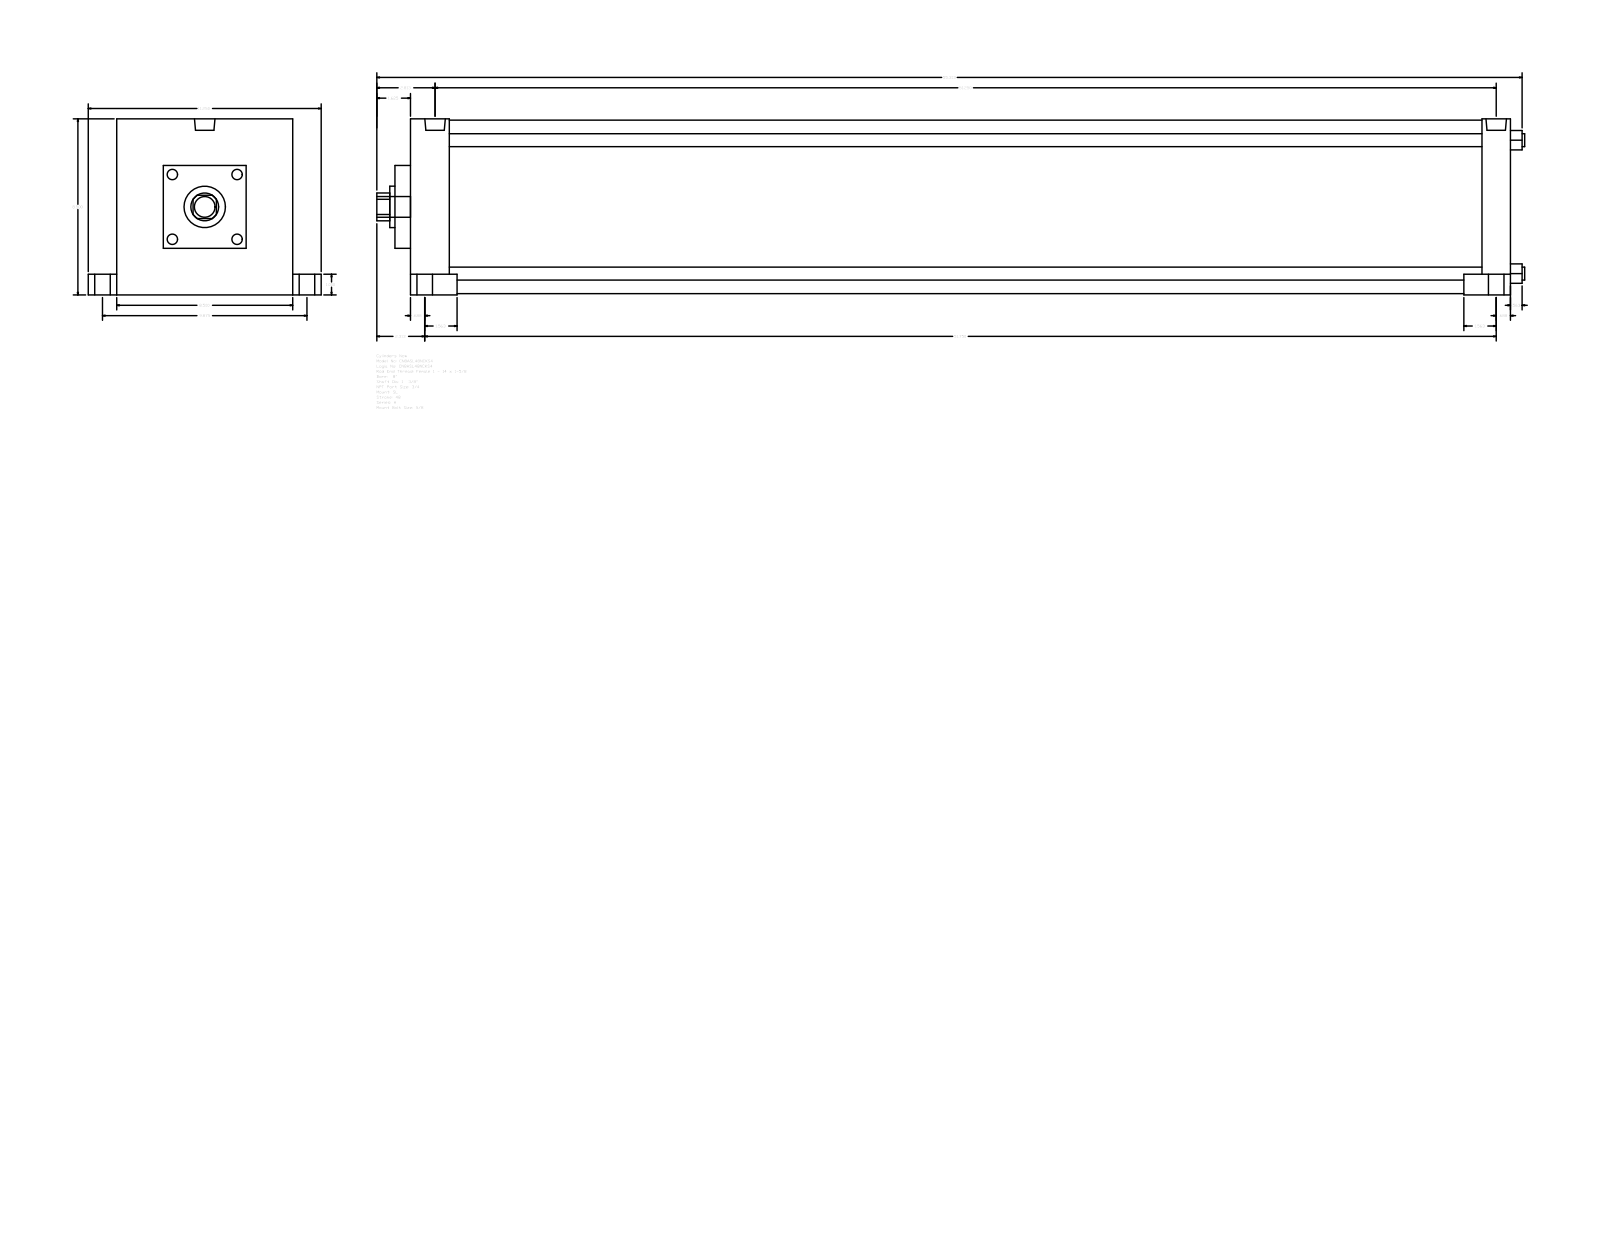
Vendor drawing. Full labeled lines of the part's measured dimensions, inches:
Part name (STEP PRODUCT): A_SL__0800_1.375
STEP written by: GSSL Pune (CONFIG_CONTROL_DESIGN)
Units: inches
Bodies: 0 solids, 117 faces (85 planar, 32 cylindrical, 0 other)
Overall size (bounding box): 55.437 × 11.25 × 8.5
Round holes (diameter × count): ⌀0.625 ×4, ⌀1.375 ×1, ⌀2 ×1, ⌀8.375 ×1
Round bosses / shafts (diameter × count): ⌀1 ×5, ⌀0.75 ×4, ⌀0.594 ×4, ⌀0.989 ×2
Partial cylindrical surfaces — rounded edges, fillets, slot ends (radius × count): R0.672 ×1
Main face-to-face distances: 53.125, 8.5, 1.375, 2.25, 1.875, 51.25, 51.75, 49.875, 0.75, 2.625
Hole centre spacings: 4.554, 6.44, 9.108
